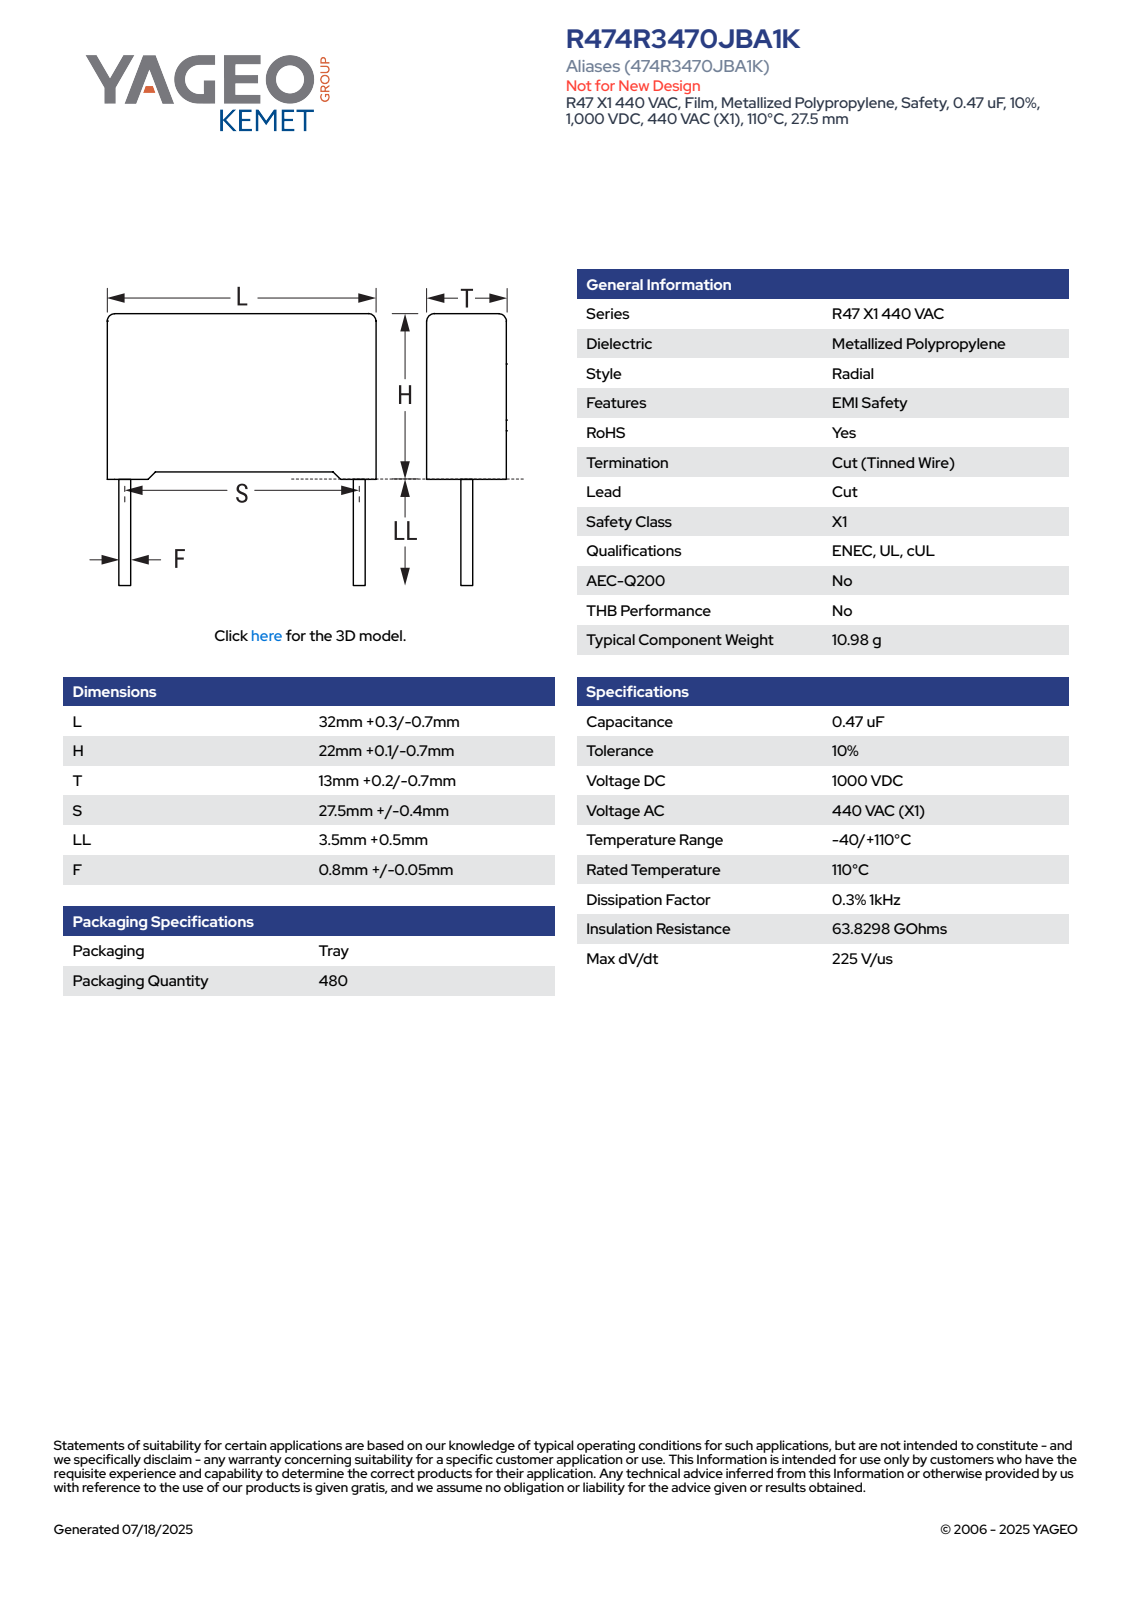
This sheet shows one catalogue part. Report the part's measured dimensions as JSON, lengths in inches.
{"part_name": "CFR_RB2_32X22X13_L32.3H22.1T13.2S27.5LL4F0.85", "step_written_by": "SolidWorks 2021 (AUTOMOTIVE_DESIGN)", "units": "inches", "bodies": {"solids": 4, "faces": 85, "planar": 77, "cylindrical": 8, "other": 0}, "overall_size": [1.272, 1.028, 0.52], "volume_in3": 0.557, "surface_area_in2": 4.555, "round_bosses_or_shafts": [[0.033, 2]], "partial_cylinders_radius": [[0.02, 4]], "face_to_face_distances": [0.52, 0.84, 1.272, 0.841, 0.03, 0.03, 0.87, 0.043, 0.52, 1.229]}
